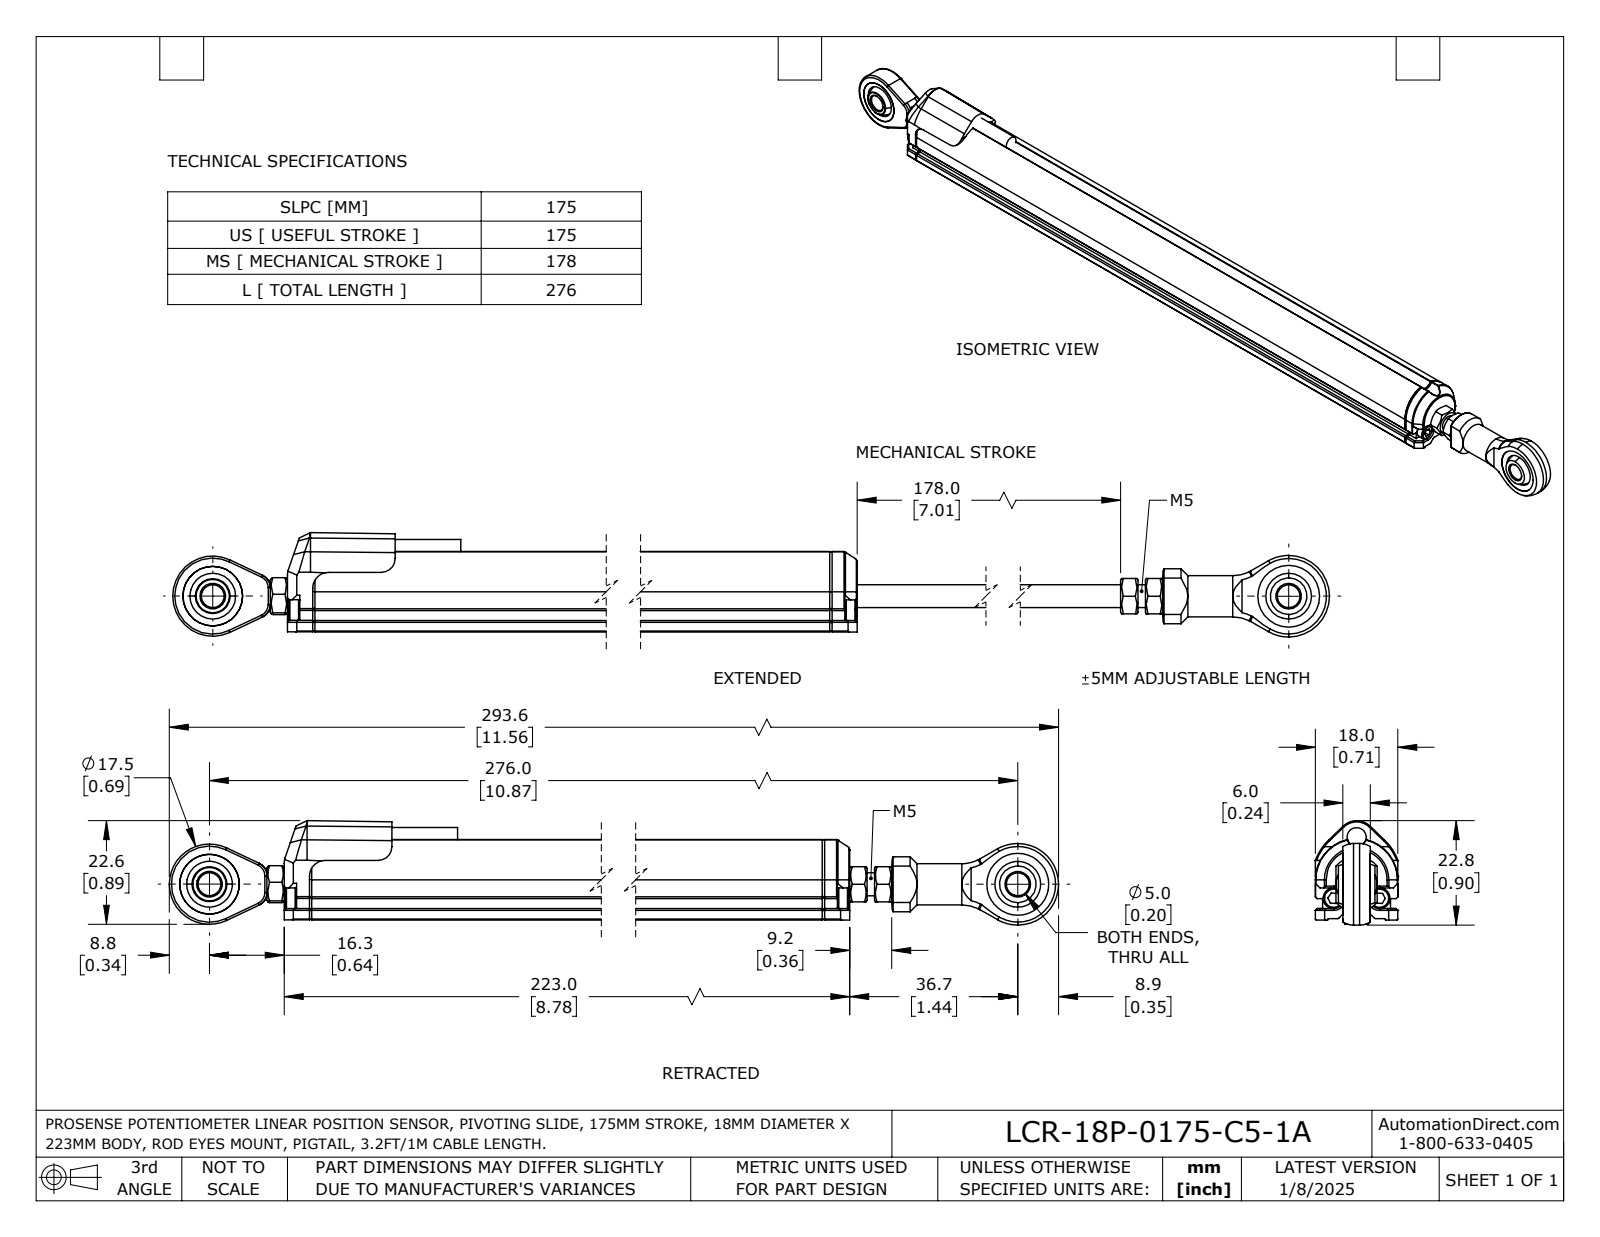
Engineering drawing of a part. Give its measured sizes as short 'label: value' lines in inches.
name: LCR-18P-0175-C5-1A
written by: SolidWorks 2023 (AUTOMOTIVE_DESIGN)
unit: in
bodies: 20 solids, 515 faces (289 planar, 136 cylindrical, 90 other)
size: 11.561 × 0.896 × 0.709
volume: 3.952 in³; area: 42.5 in²
holes: 4× ⌀0.197, 2× ⌀0.102, 2× ⌀0.104, 2× ⌀0.394, 1× ⌀0.213, 1× ⌀0.272, 1× ⌀0.512, 1× ⌀0.531
bosses: 4× ⌀0.181, 3× ⌀0.113, 2× ⌀0.059, 1× ⌀0.354, 1× ⌀0.165, 1× ⌀0.113
rounds: 12× R0.008, 10× R0.004, 8× R0.02, 6× R0.012, 6× R0.018, 4× R0.016, 4× R0.039, 4× R0.043
face distances: 0.709, 0.02, 0.059, 0.071, 0.063, 0.646, 8.327, 0.236, 0.087, 0.098
hole spacings: 0.231, 0.394, 0.23, 0.231, 10.866
